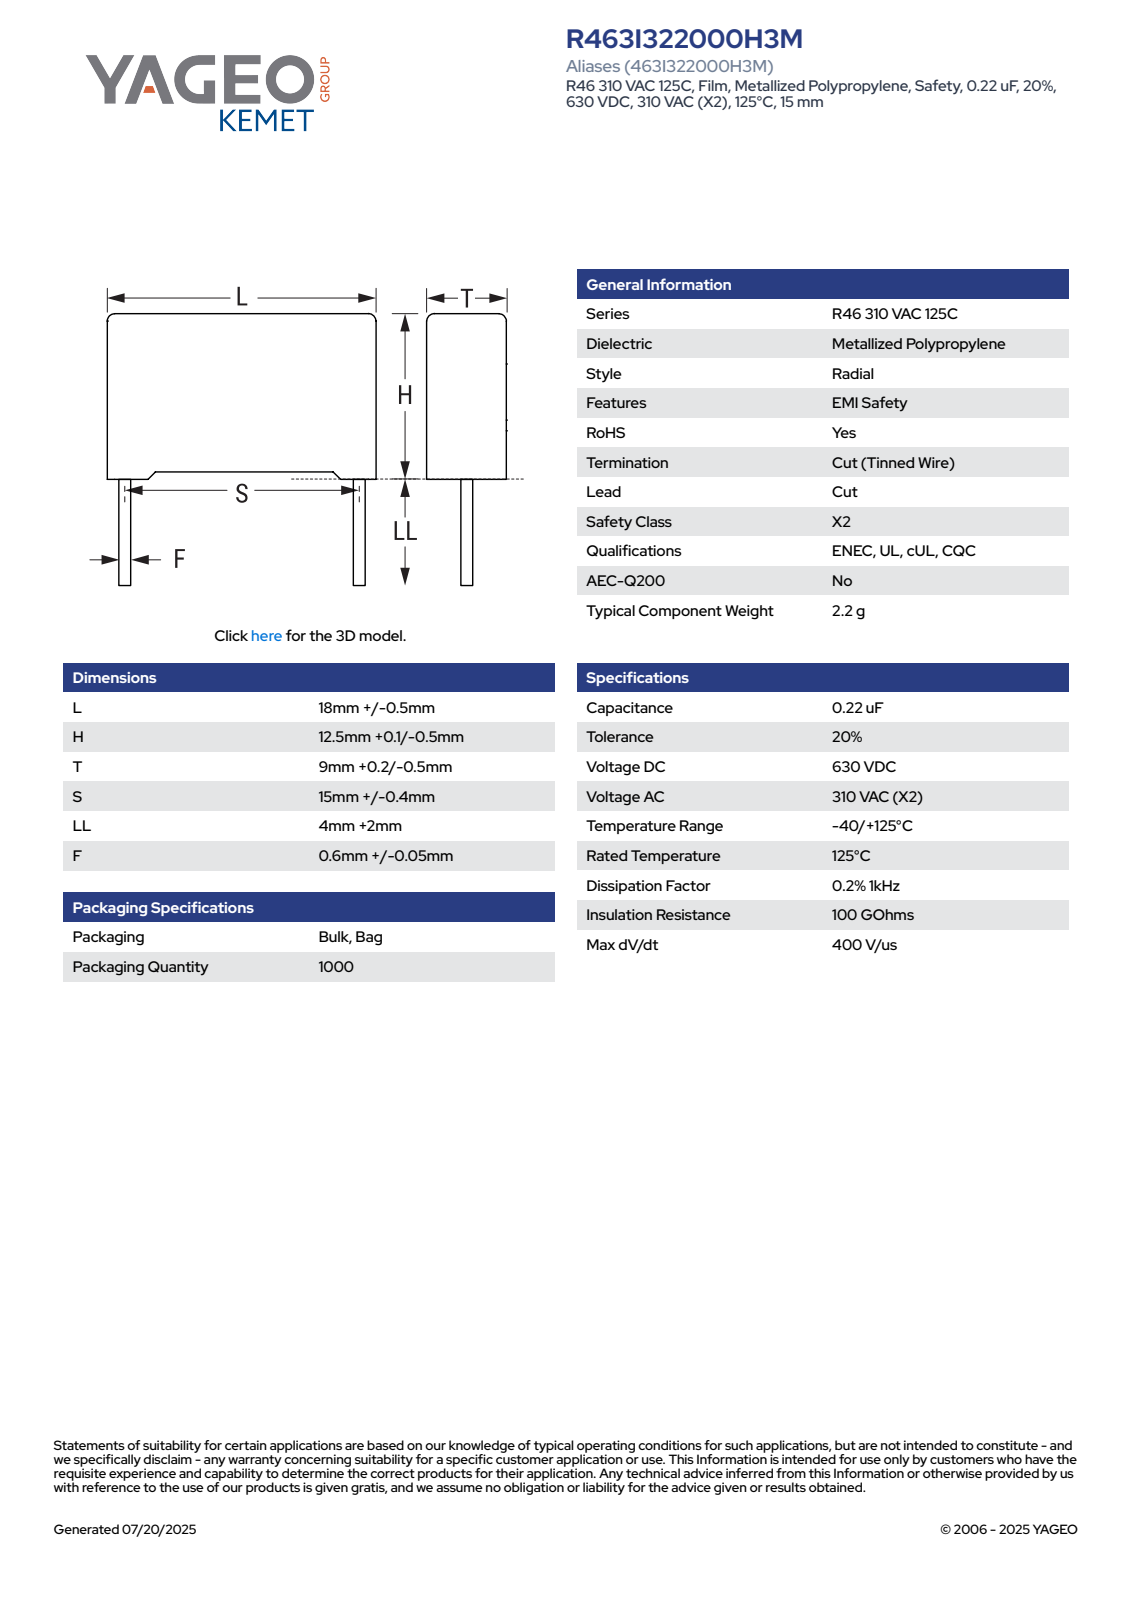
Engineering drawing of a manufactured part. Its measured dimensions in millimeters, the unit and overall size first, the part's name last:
Units: millimetres
Overall size (bounding box): 18.6 × 18 × 9.21
Round bosses / shafts (diameter × count): ⌀0.65 ×2
Partial cylindrical surfaces — rounded edges, fillets, slot ends (radius × count): R0.5 ×4
Main face-to-face distances: 9.2, 11.85, 18, 0.6, 0.75, 12.6, 8.6, 0.43, 0.32, 12.17
Volume: 1 981 mm³ · Surface area: 1 074 mm²
Bodies: 4 solids, 85 faces (77 planar, 8 cylindrical, 0 other)
Part name (STEP PRODUCT): CFR_RB2_18X17.5X6_L18.5H12.6T9.2S15LL6F0.65
STEP written by: SolidWorks 2021 (AUTOMOTIVE_DESIGN)
